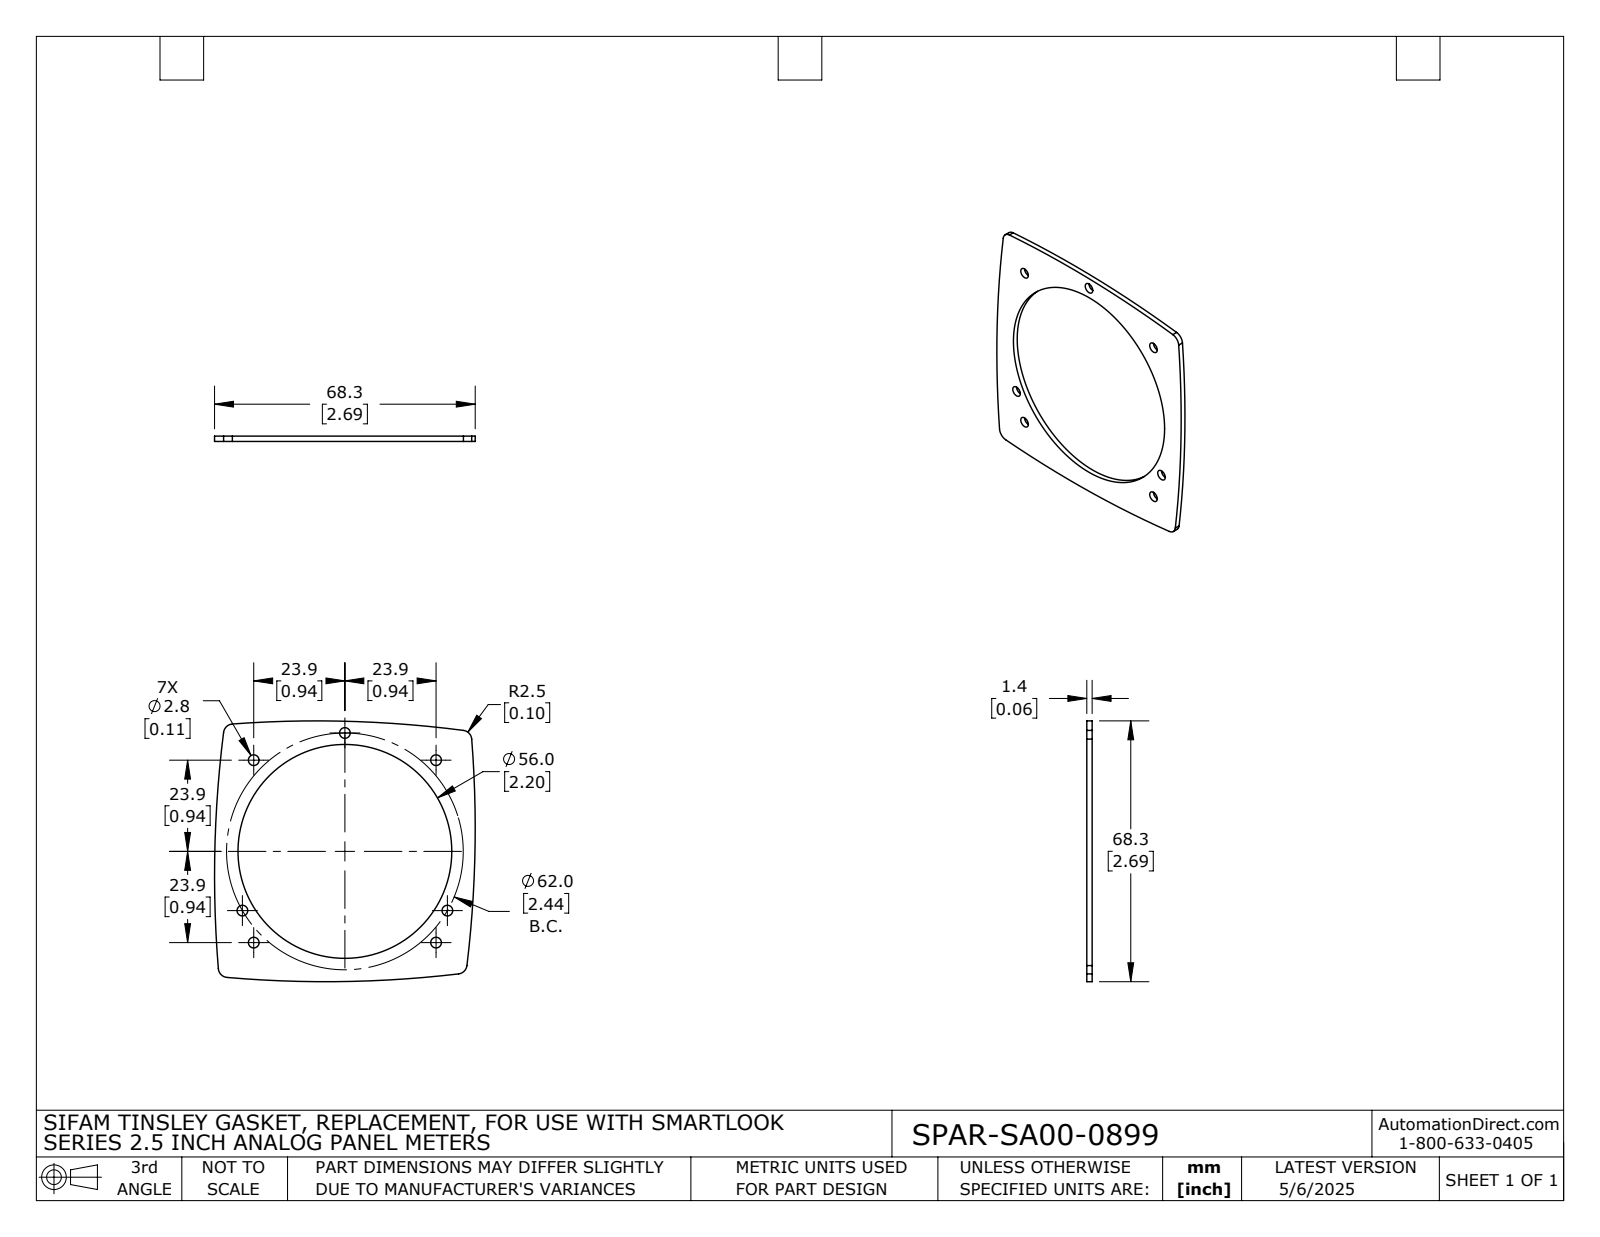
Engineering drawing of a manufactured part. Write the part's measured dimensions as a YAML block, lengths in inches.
part_name: "SPAR-SA00-0899"
step_written_by: "SolidWorks 2021 (AUTOMOTIVE_DESIGN)"
units: inches
bodies: {solids: 1, faces: 27, planar: 2, cylindrical: 25, other: 0}
overall_size: [2.688, 2.688, 0.055]
volume: 0.168
surface_area: 7.182
round_holes:
  - {diameter: 0.11, count: 7}
  - {diameter: 2.205, count: 1}
partial_cylinders:
  - {radius: 0.098, count: 4}
  - {radius: 11.744, count: 4}
face_to_face_distances: [0.055]
hole_center_spacings: [1.33, 1.88, 1.22, 2.114, 0.35, 0.981, 1.555, 2.024]
